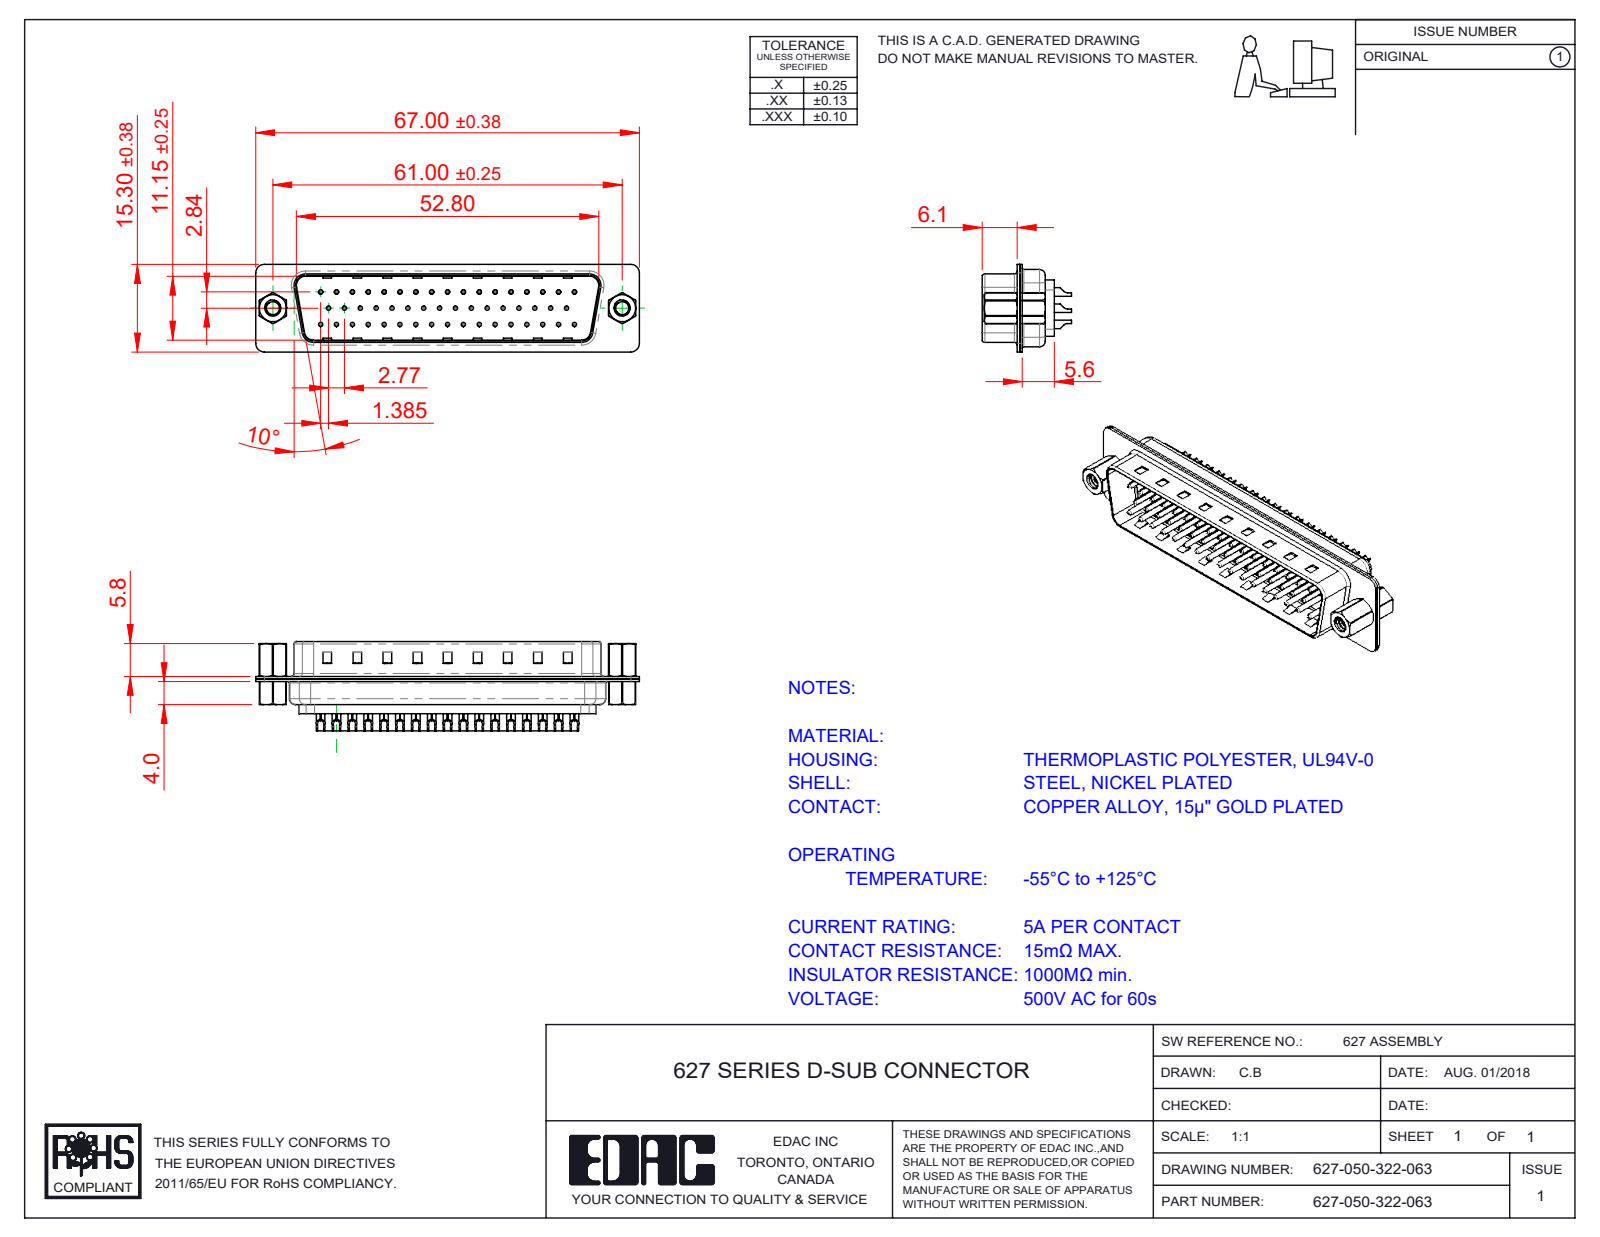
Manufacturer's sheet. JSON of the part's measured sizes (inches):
{"part_name": "627 Contact Row 1_22L; 627-050-322-063; 627 Shell Rear_50 Contacts; 627 Shell Front_50 Contacts (+5 more)", "step_written_by": "SolidWorks 2020 (CONFIG_CONTROL_DESIGN)", "units": "inches", "bodies": {"solids": 57, "faces": 3734, "planar": 925, "cylindrical": 1661, "other": 1148}, "overall_size": [2.638, 0.614, 0.602], "volume_in3": 0.284, "surface_area_in2": 20.53, "round_holes": [[0.063, 58], [0.014, 50], [0.043, 50], [0.03, 8], [0.079, 8], [0.089, 2], [0.09, 2], [0.157, 2], [0.189, 2]], "round_bosses_or_shafts": [[0.079, 50], [0.059, 50], [0.03, 50], [0.197, 2], [0.193, 2], [0.11, 2]], "partial_cylinders_radius": [[0.059, 16], [0.079, 12], [0.02, 8], [0.063, 8], [0.039, 7], [0.01, 4], [0.024, 4], [0.026, 4]], "face_to_face_distances": [0.016, 0.018, 0.455, 0.035, 0.238, 0.256, 0.031, 0.077, 0.03, 0.485], "hole_center_spacings": [0.109, 0.124, 0.218, 0.327, 0.436, 0.545, 0.654, 0.763]}
